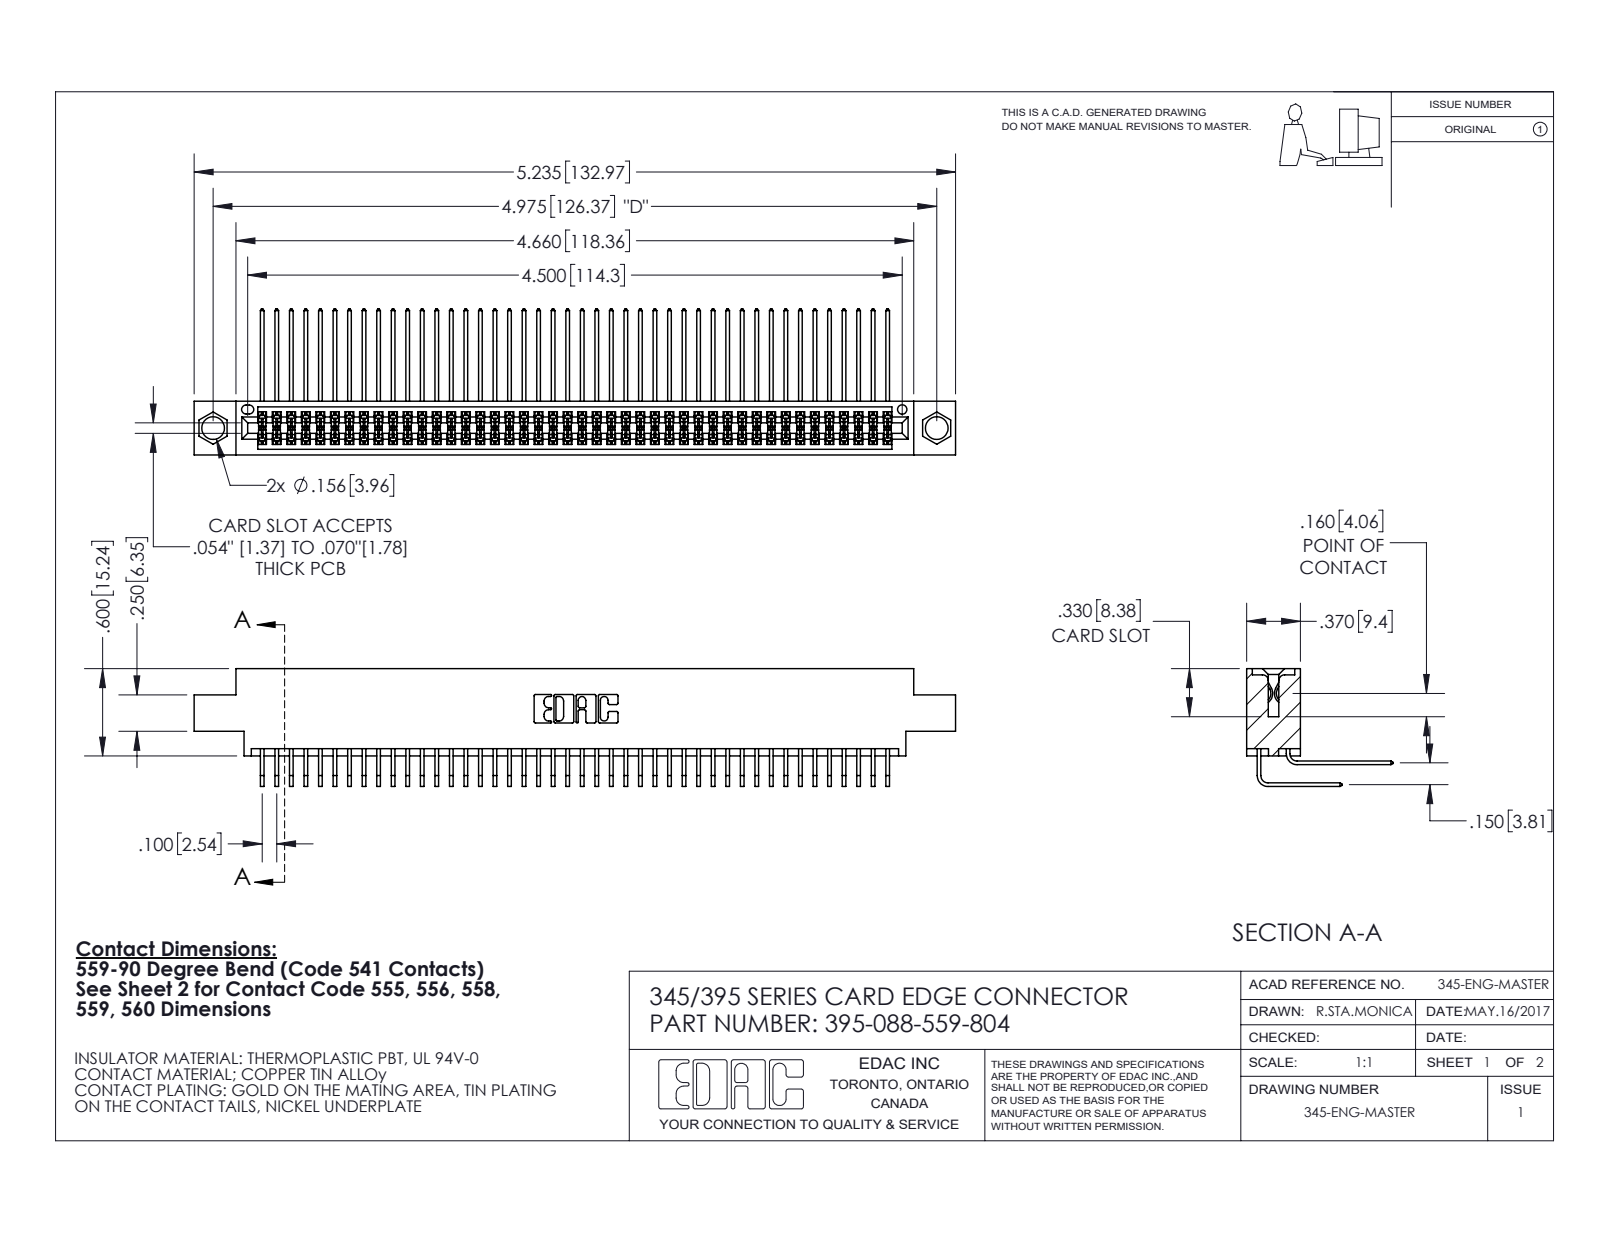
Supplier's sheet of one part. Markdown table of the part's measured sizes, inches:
| quantity | value |
| --- | --- |
| part name | 345-292-001_559 Tail - 2; 345-292-001_558 559 Tail - 1; 395-088-559-804; 345 Part_0.170 Offset - 0.156 Dia-TI |
| STEP written by | SolidWorks 2020 (CONFIG_CONTROL_DESIGN) |
| units | inches |
| bodies | 89 solids, 4720 faces (3178 planar, 1542 cylindrical, 0 other) |
| overall size | 5.235 × 1.005 × 0.809 |
| volume | 0.807 in³ |
| surface area | 34.05 in² |
| round holes (diameter × count) | 0.156 × 2, 0.064 × 1 |
| partial cylindrical surfaces (radius × count) | 0.006 × 176, 0.01 × 22, 0.007 × 6, 0.031 × 6, 0.026 × 3, 0.014 × 2, 0.019 × 2, 0.022 × 2 |
| main face-to-face distances | 0.072, 0.298, 0.37, 0.2, 0.098, 0.272, 0.025, 0.225, 0.175, 0.15 |
| hole center spacings | 0.27, 4.739, 4.975 |
